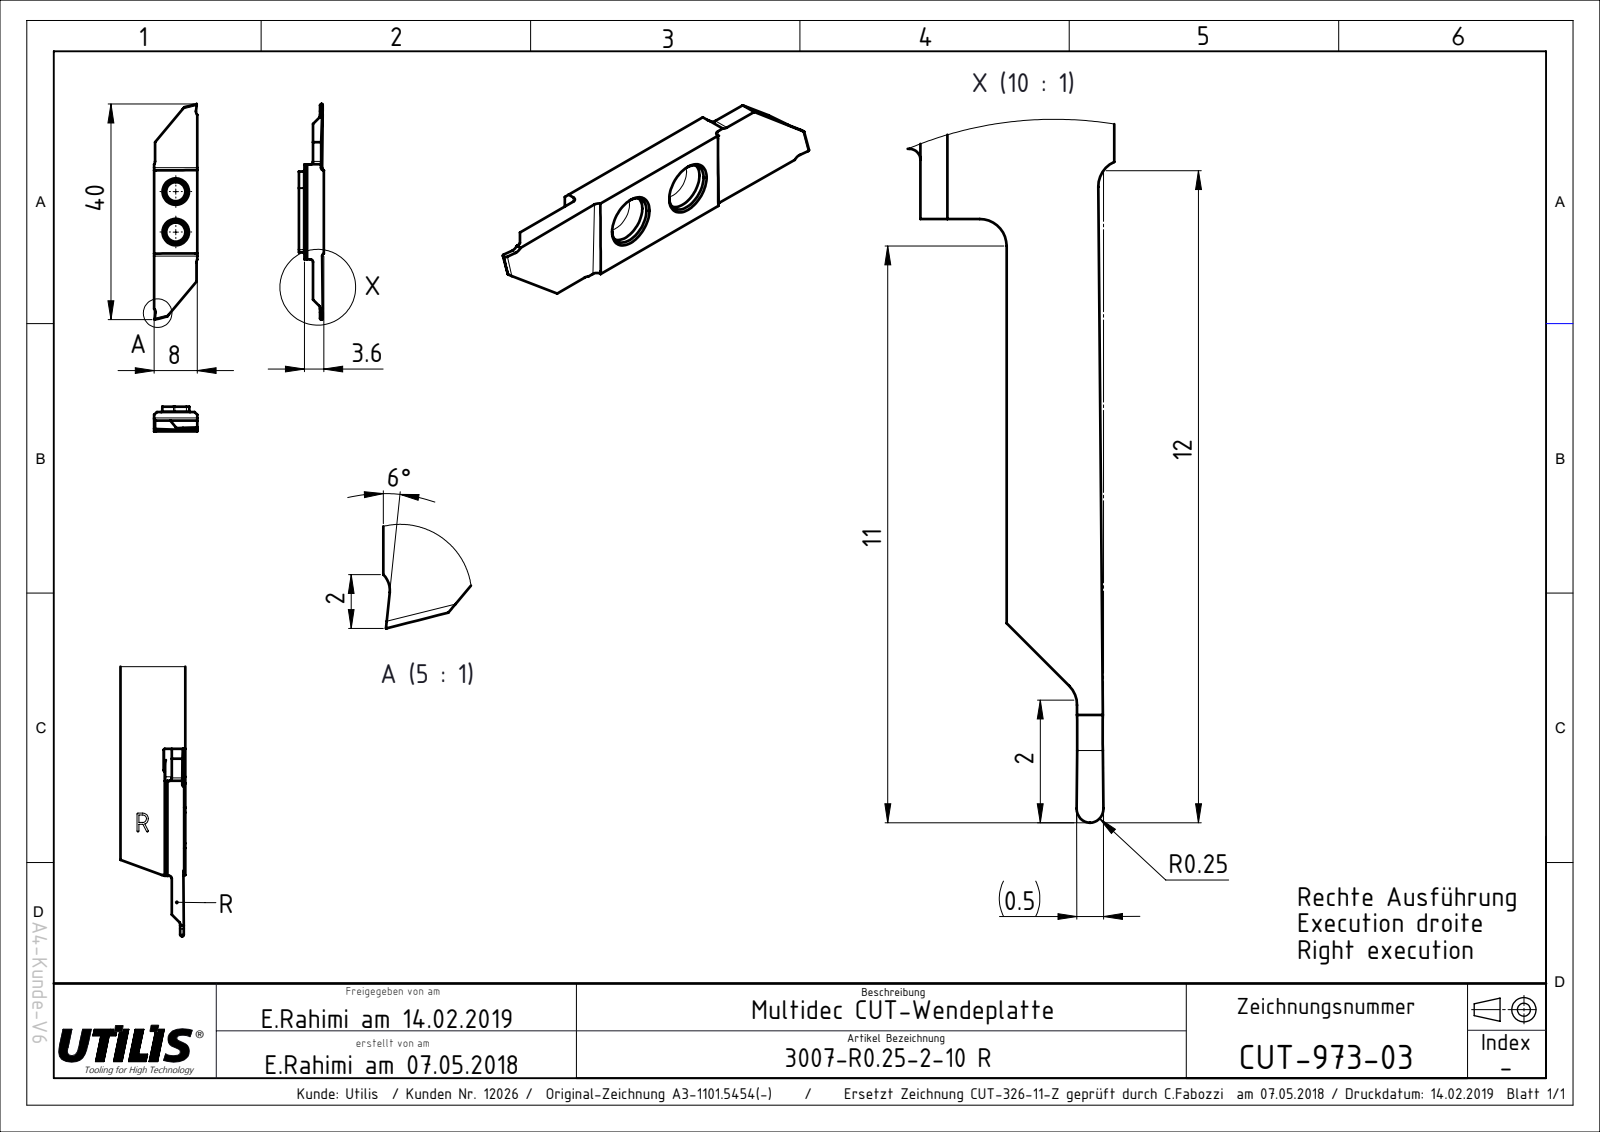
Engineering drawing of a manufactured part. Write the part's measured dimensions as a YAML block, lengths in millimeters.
part_name: "CUT-973; ASME Y14.5"
step_written_by: "FormatWorks Professional (AP242_MANAGED_MODEL_BASED_3D_ENGINEERING_MIM_LF)"
units: millimeters
bodies: {solids: 1, faces: 42, planar: 24, cylindrical: 18, other: 0}
overall_size: [40, 8, 3.6]
volume: 635
surface_area: 802
round_holes:
  - {diameter: 3.55, count: 2}
partial_cylinders:
  - {radius: 0.5, count: 6}
  - {radius: 0.25, count: 2}
  - {radius: 0.8, count: 2}
  - {radius: 1, count: 2}
face_to_face_distances: [3.6, 1.6, 2, 8, 7.85, 22.54, 17.6, 7.7, 7.58, 11.2]
hole_center_spacings: [7.5]
